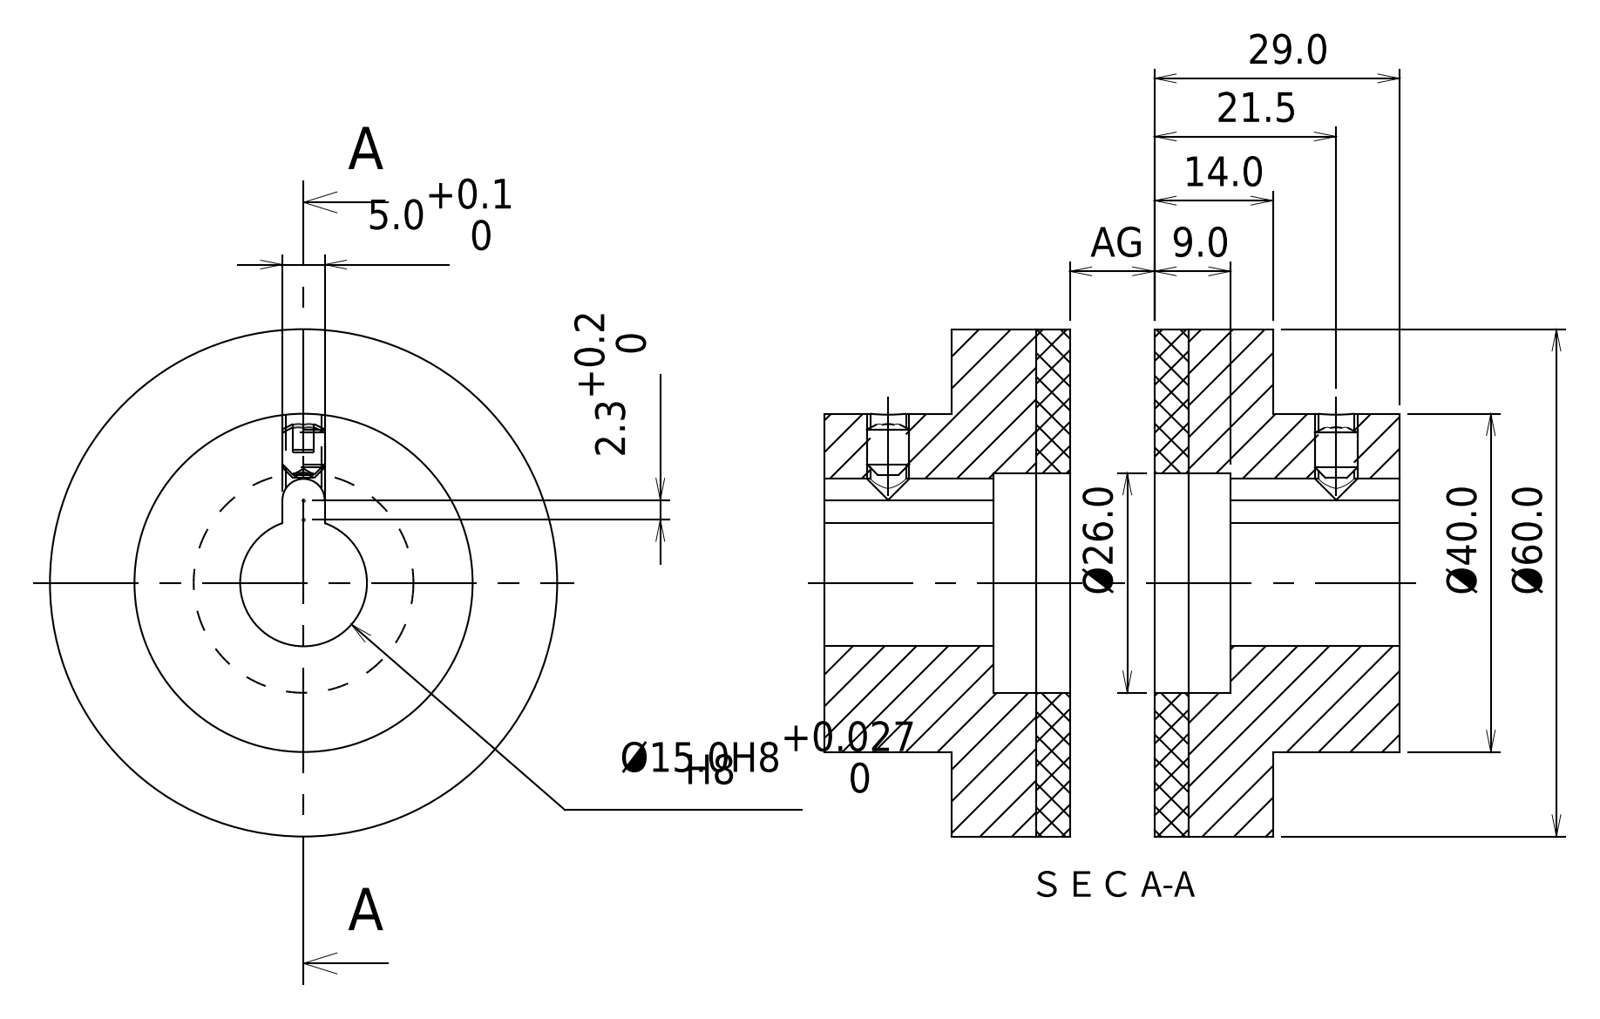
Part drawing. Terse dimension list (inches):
written by: PSStep 10.0 (CONFIG_CONTROL_DESIGN)
unit: in
bodies: 4 solids, 38 faces (22 planar, 10 cylindrical, 6 other)
size: 2.362 × 2.362 × 1.142
volume: 3.035 in³; area: 25.69 in²
holes: 1× ⌀0.165, 1× ⌀0.591, 1× ⌀1.024
bosses: 1× ⌀2.362, 1× ⌀1.575, 1× ⌀0.197
rounds: 1× R0.098
face distances: 0.157, 0.394, 0.551, 0.591, 0.984, 1.142, 0.197, 0.787, 0.354, 0.098
